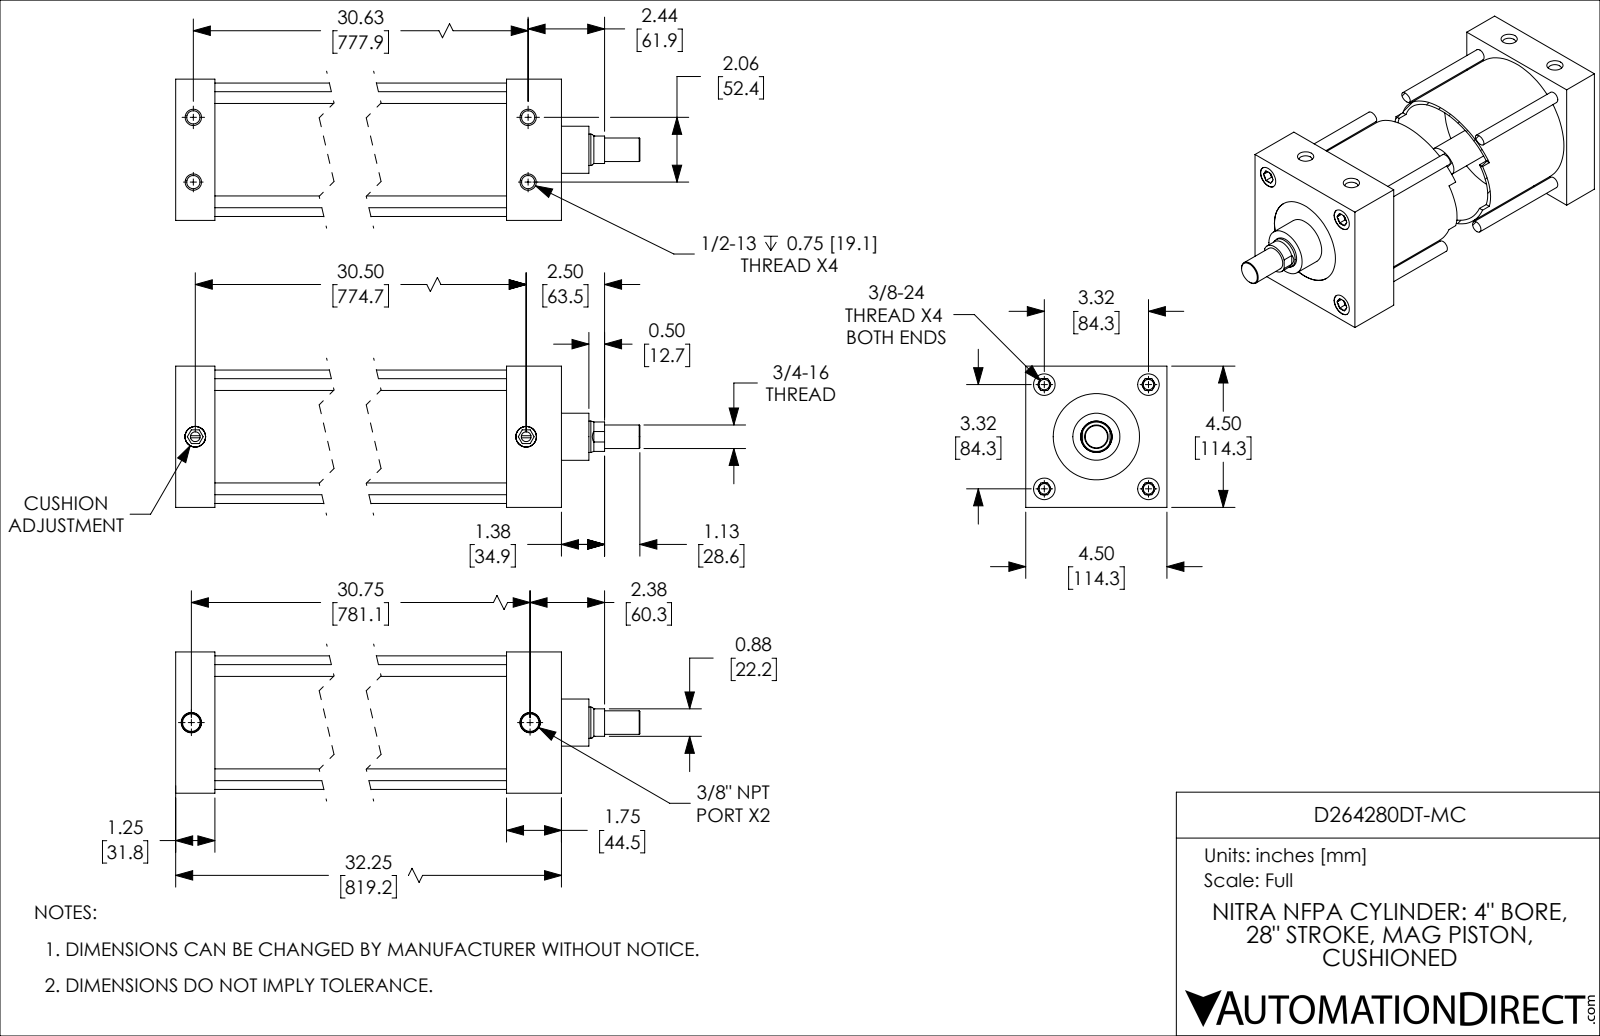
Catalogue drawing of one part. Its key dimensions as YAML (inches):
part_name: "D264280DT-MC_PISTON_KK1; D264280DT-MC_CUSHION; D264280DT-MC_BODY; D264280DT-MC"
step_written_by: "SolidWorks 2019 (CONFIG_CONTROL_DESIGN)"
units: inches
bodies: {solids: 4, faces: 246, planar: 90, cylindrical: 78, other: 78}
overall_size: [34.75, 4.5, 4.5]
volume: 158.7
surface_area: 1202
round_holes:
  - {diameter: 0.332, count: 4}
  - {diameter: 0.422, count: 4}
  - {diameter: 0.687, count: 4}
  - {diameter: 0.312, count: 2}
  - {diameter: 0.562, count: 2}
  - {diameter: 0.656, count: 2}
  - {diameter: 1.001, count: 1}
  - {diameter: 2.75, count: 1}
  - {diameter: 4.001, count: 1}
round_bosses_or_shafts:
  - {diameter: 0.375, count: 4}
  - {diameter: 0.657, count: 2}
  - {diameter: 4.251, count: 1}
  - {diameter: 3.999, count: 1}
  - {diameter: 1.5, count: 1}
  - {diameter: 0.999, count: 1}
  - {diameter: 0.75, count: 1}
partial_cylinders:
  - {radius: 0.469, count: 1}
face_to_face_distances: [1.25, 4.5, 30.5, 29.25, 32.25, 31, 1.75, 2.5, 28, 29.75]
hole_center_spacings: [1.033, 2.347, 3.32, 30.705, 2.062, 4.695, 30.625, 30.694]
